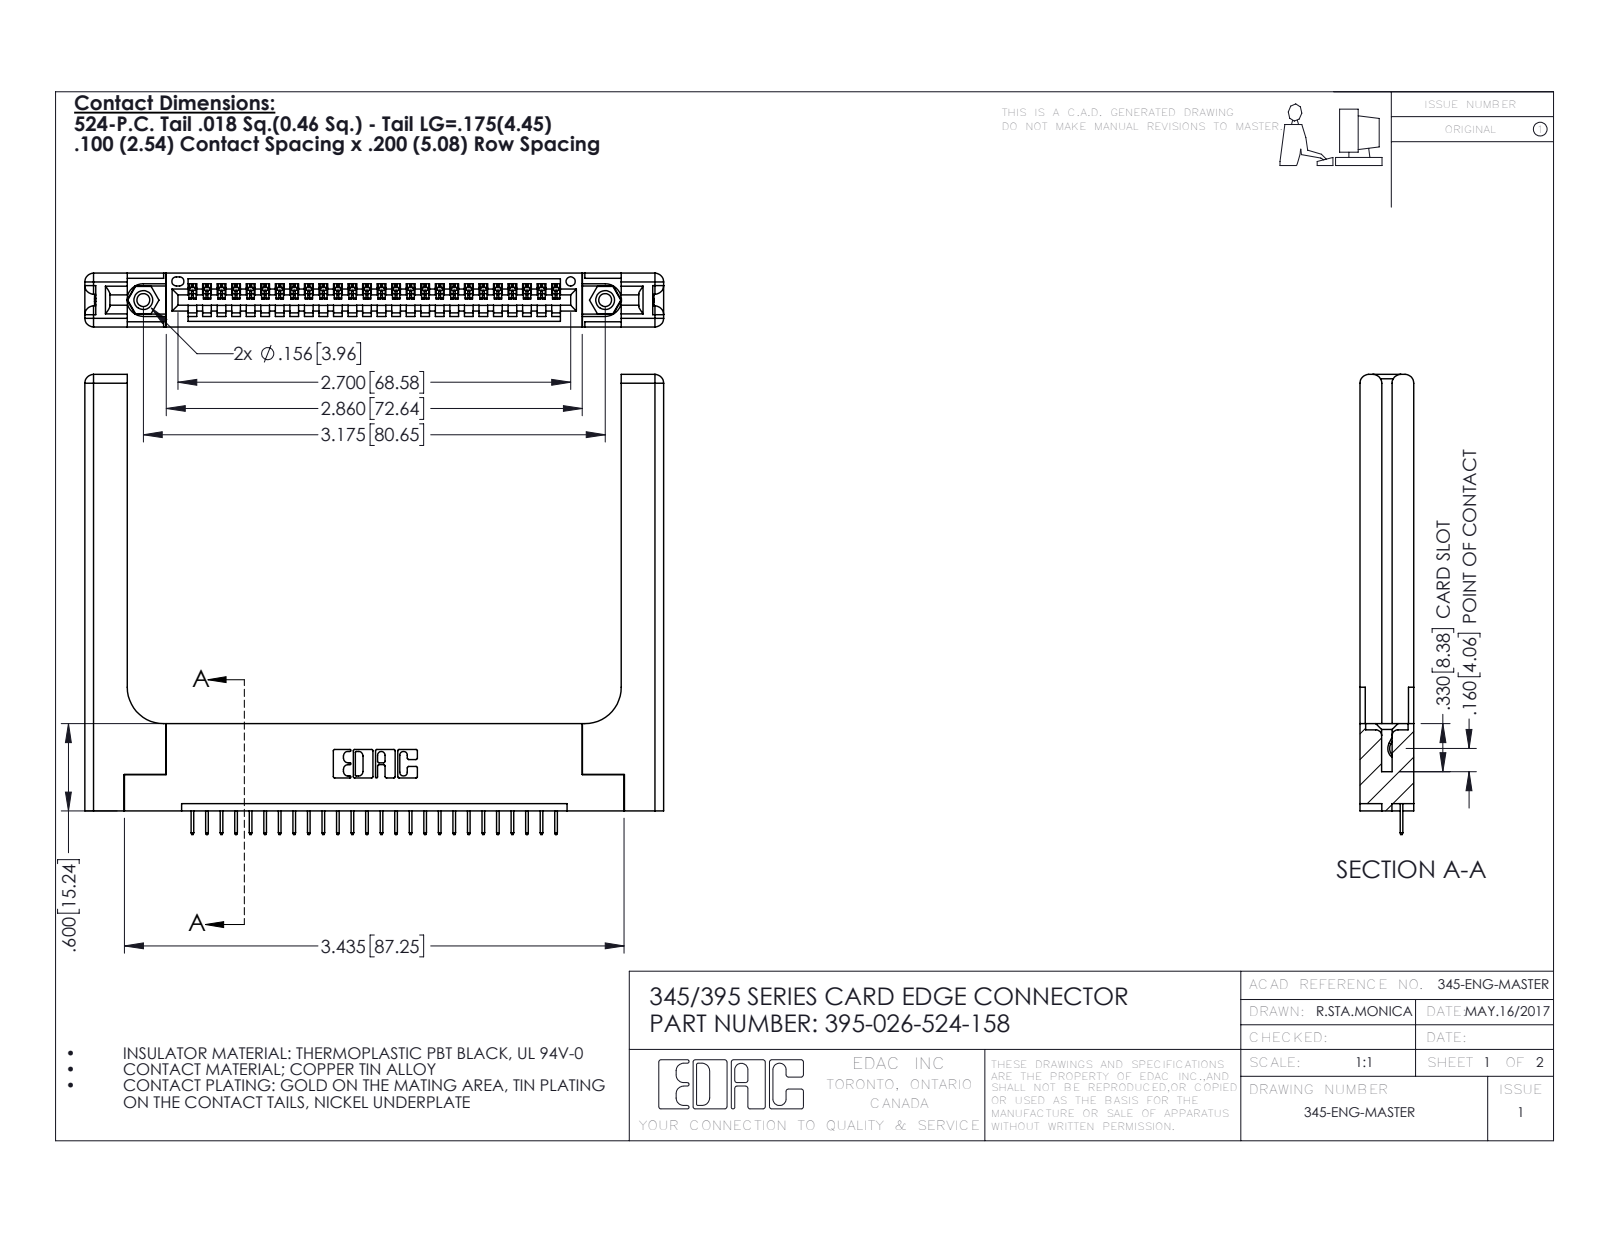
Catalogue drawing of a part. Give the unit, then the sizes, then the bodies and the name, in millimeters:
Units: millimetres
Overall size (bounding box): 101.1 × 80.3 × 9.4
Round holes (diameter × count): ⌀2.3 ×2, ⌀3.2 ×2, ⌀4 ×2, ⌀1.6 ×1
Round bosses / shafts (diameter × count): ⌀3.9 ×2
Partial cylindrical surfaces — rounded edges, fillets, slot ends (radius × count): R0.2 ×52, R0.3 ×22, R1.5 ×16, R0.2 ×6, R0.8 ×6, R0.7 ×3, R0.8 ×2, R0.8 ×2
Main face-to-face distances: 9.4, 1.8, 7.6, 5.1, 3.8, 3.8, 2, 5.6, 2.5, 6.9
Hole centre spacings: 6.9, 74.7, 80.6
Volume: 17 880 mm³ · Surface area: 17 210 mm²
Bodies: 31 solids, 1994 faces (1424 planar, 510 cylindrical, 60 other)
Part name (STEP PRODUCT): 395-026-524-158; 345-292-001_345-293-124; 345-250-001_345-250-001-102; 345 Part_Flush Mounting Lugs - 0.156 Dia-TH (+1 more)
STEP written by: SolidWorks 2016 (CONFIG_CONTROL_DESIGN)
